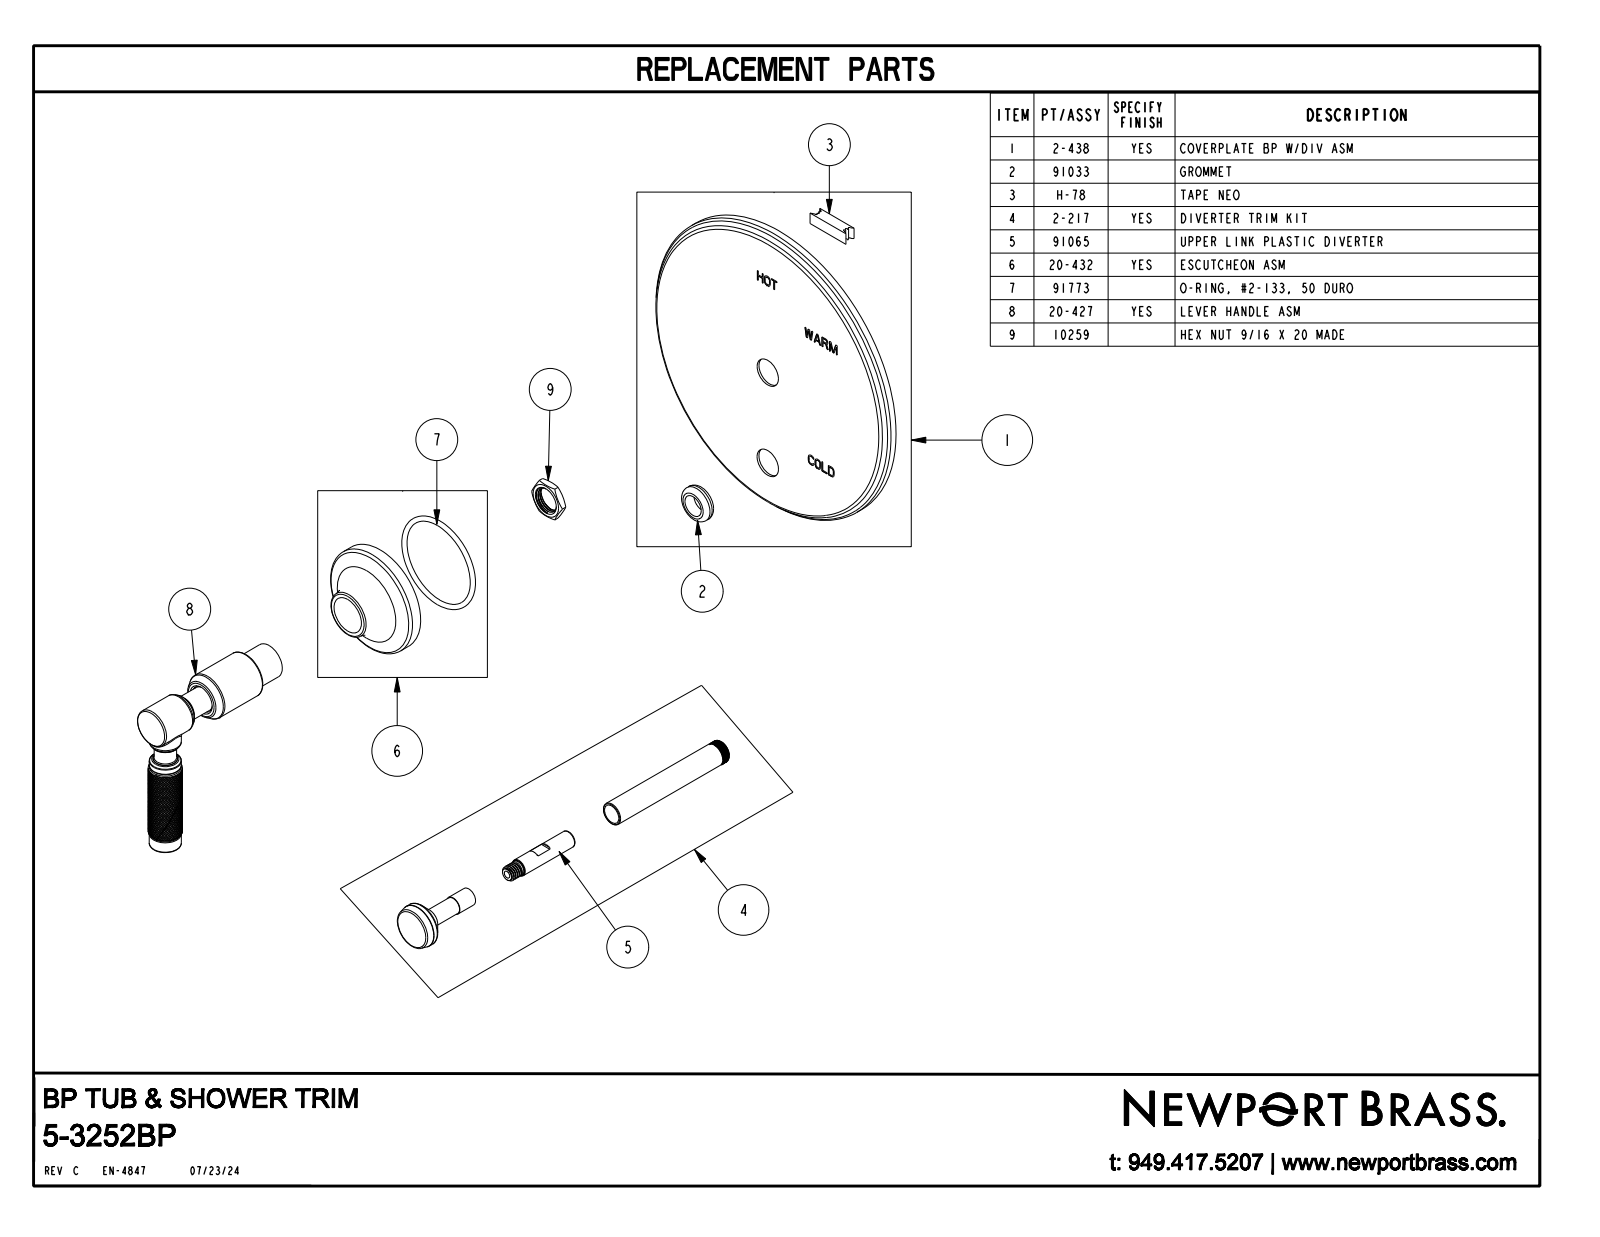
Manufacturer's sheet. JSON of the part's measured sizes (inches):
{"part_name": "5-3252BP", "step_written_by": "CREO PARAMETRIC BY PTC INC, 2023134 (CONFIG_CONTROL_DESIGN)", "units": "inches", "bodies": {"solids": 1, "faces": 5490, "planar": 283, "cylindrical": 1035, "other": 4172}, "overall_size": [6.5, 6.5, 3.984], "volume_in3": 5.847, "surface_area_in2": 104.6, "round_holes": [[0.394, 1], [0.59, 1], [0.594, 1], [0.76, 1], [1.7, 1], [6.4, 1]], "round_bosses_or_shafts": [[6.5, 1], [2.25, 1], [0.965, 1], [0.9, 1], [0.85, 1], [0.787, 1], [0.73, 1], [0.67, 1]], "face_to_face_distances": [0.05, 0.25, 0.3, 0.263, 0.313, 0.563, 0.27, 1.565, 1.302, 1.252], "hole_center_spacings": [2.17]}
